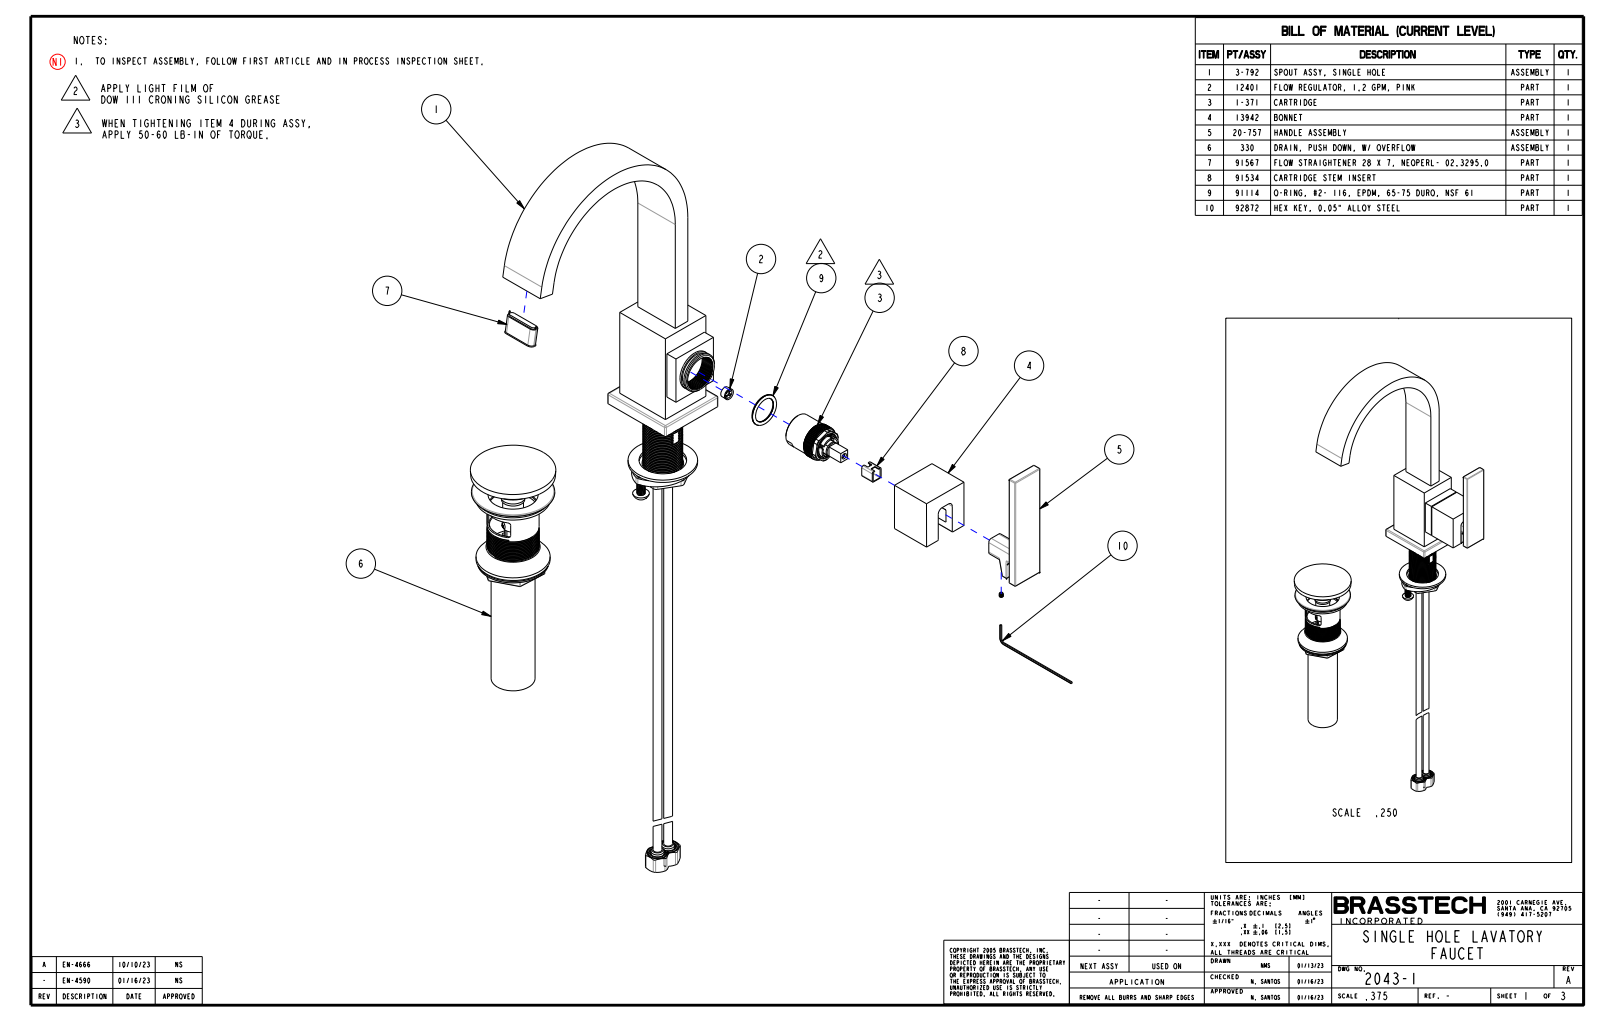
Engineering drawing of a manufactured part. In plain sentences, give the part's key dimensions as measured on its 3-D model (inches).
The part is named "13940; 30611; 12167; 20-756_ASM (+8 more)". Its 3-D file was written by "CREO PARAMETRIC BY PTC INC, 2023134 (CONFIG_CONTROL_DESIGN)". It is 20 solids with 1636 faces: 569 planar, 638 cylindrical and 429 other. Overall it measures 9.712 by 6.724 by 4.354 inches. Its volume is 15.46 cubic inches and its surface area 266.7 square inches. Round holes: 4 of diameter 0.156, 3 of diameter 0.2, 3 of diameter 0.222, 3 of diameter 0.303, 2 of diameter 0.139, 2 of diameter 0.205, 2 of diameter 0.375, 1 of diameter 0.089, 1 of diameter 0.13, 1 of diameter 0.14, 1 of diameter 0.145, 1 of diameter 0.157. Round bosses or shafts: 4 of diameter 0.094, 4 of diameter 0.07, 3 of diameter 0.164, 2 of diameter 0.27, 2 of diameter 0.152, 2 of diameter 0.123, 1 of diameter 1.175, 1 of diameter 1.087. Partial cylindrical surfaces (rounded edges, fillets, slot ends): 20 of radius 0.04, 19 of radius 0.02, 16 of radius 0.125, 12 of radius 0.01, 12 of radius 0.05, 12 of radius 0.063, 8 of radius 0.019, 8 of radius 0.118. The main face-to-face distances are 0.062, 0.438, 0.25, 0.5, 1.438, 0.376, 0.56, 1.5, 0.622, 0.998. The hole center spacings are 0.216, 0.368, 0.41, 0.362, 0.374, 0.067, 0.198, 0.213.
